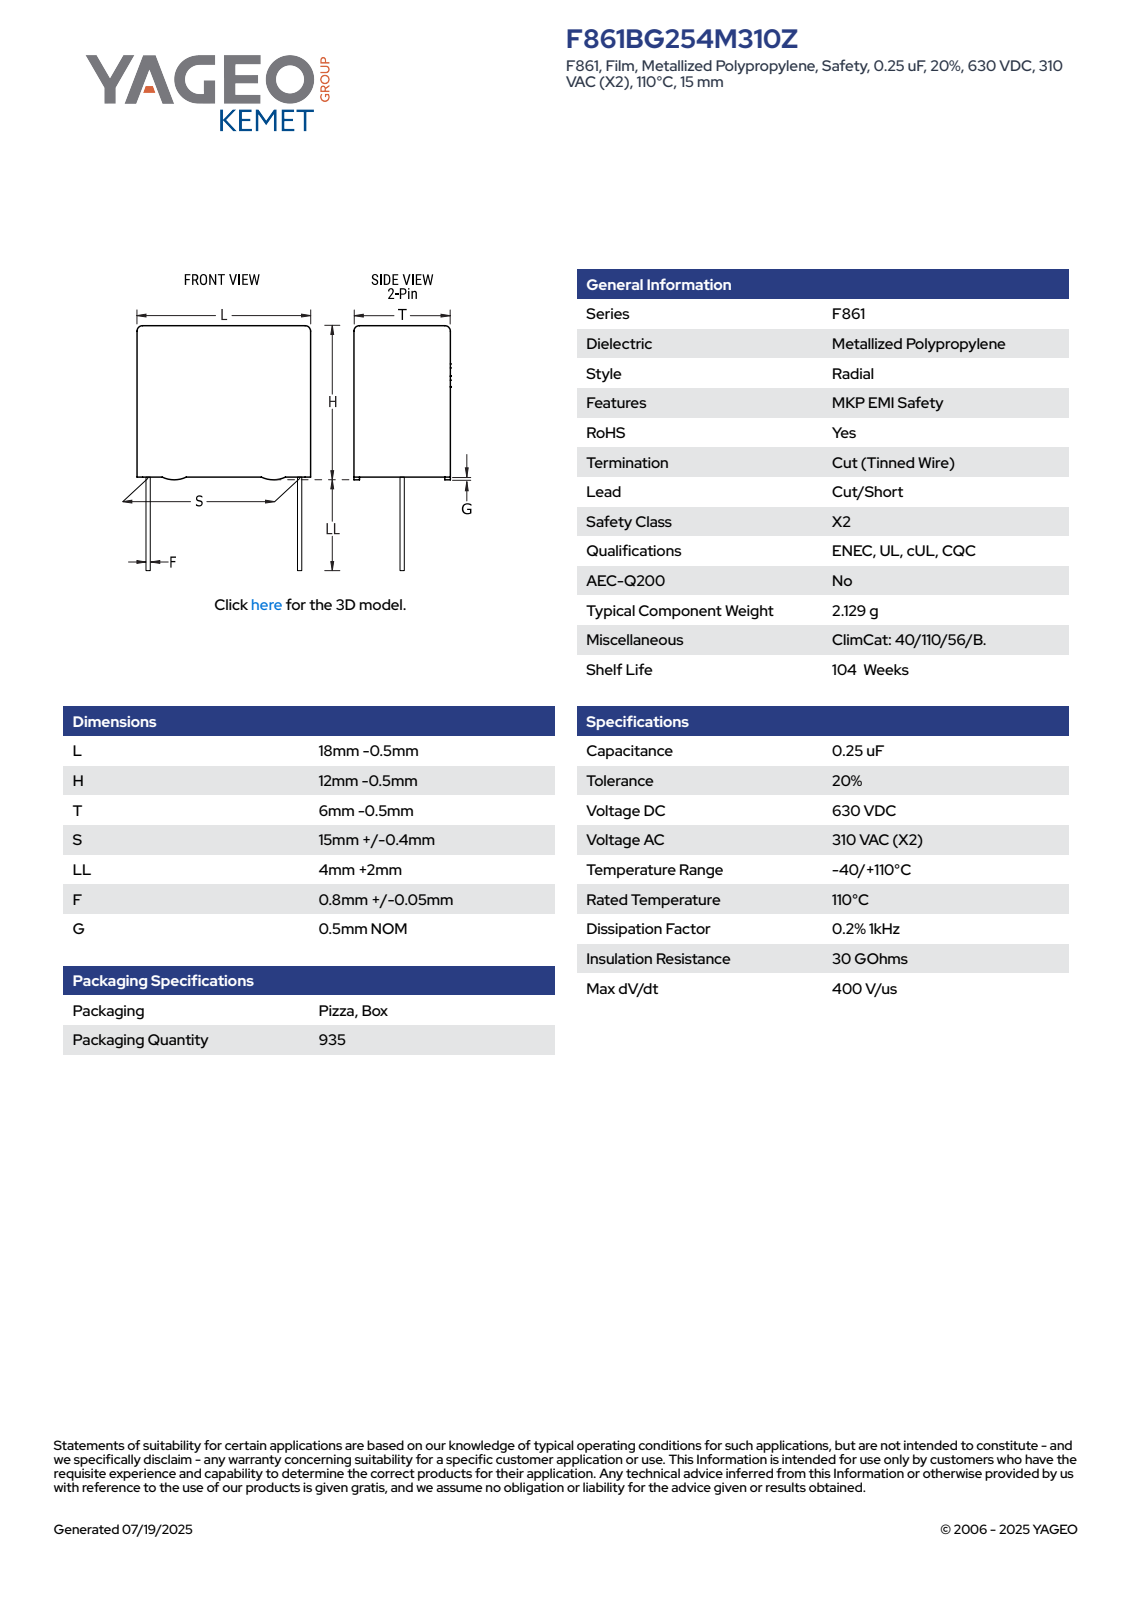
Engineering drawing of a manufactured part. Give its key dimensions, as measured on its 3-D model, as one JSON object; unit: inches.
{"part_name": "CFR_RBG_18X12X6_L17.5H11.5T5.5S15LL6F0.85G0.5", "step_written_by": "SolidWorks 2014 (AUTOMOTIVE_DESIGN)", "units": "inches", "bodies": {"solids": 4, "faces": 89, "planar": 81, "cylindrical": 8, "other": 0}, "overall_size": [0.689, 0.689, 0.217], "volume_in3": 0.065, "surface_area_in2": 1.19, "round_bosses_or_shafts": [[0.033, 2]], "partial_cylinders_radius": [[0.02, 4]], "face_to_face_distances": [0.217, 0.433, 0.689, 0.012, 0.204, 0.02, 0.453, 0.192, 0.236, 0.256]}
